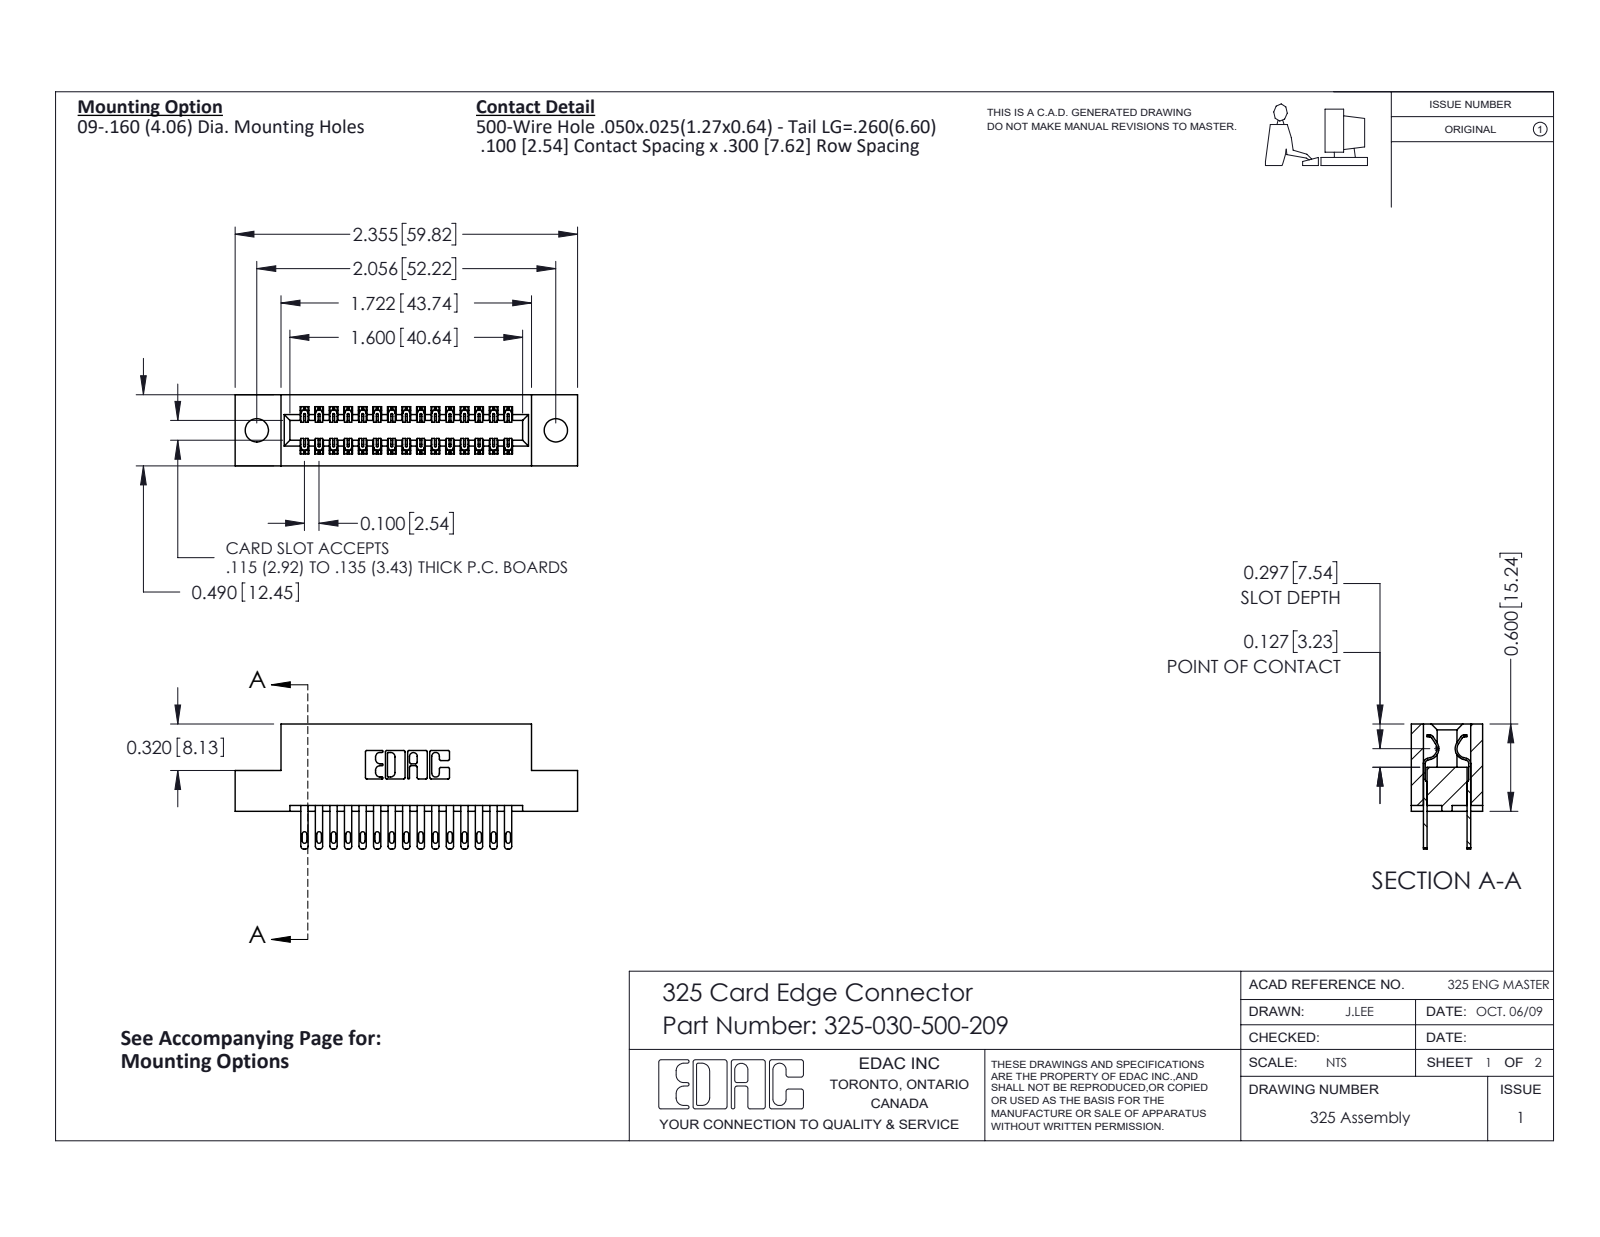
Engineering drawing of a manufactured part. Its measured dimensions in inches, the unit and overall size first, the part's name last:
Units: inches
Overall size (bounding box): 2.355 × 0.86 × 0.49
Round holes (diameter × count): ⌀0.16 ×2
Partial cylindrical surfaces — rounded edges, fillets, slot ends (radius × count): R0.006 ×45, R0.016 ×30, R0.02 ×30, R0.01 ×22, R0.007 ×6, R0.031 ×6, R0.026 ×3, R0.014 ×2
Main face-to-face distances: 0.083, 0.407, 0.3, 0.107, 0.383, 0.025, 0.49, 0.325, 0.04, 0.1
Hole centre spacings: 2.056
Volume: 0.448 in³ · Surface area: 13.14 in²
Bodies: 31 solids, 1554 faces (970 planar, 584 cylindrical, 0 other)
Part name (STEP PRODUCT): 325-292-001_325-293-100; 325 Part_.160 TH; 325-030-500-209
STEP written by: SolidWorks 2016 (CONFIG_CONTROL_DESIGN)
